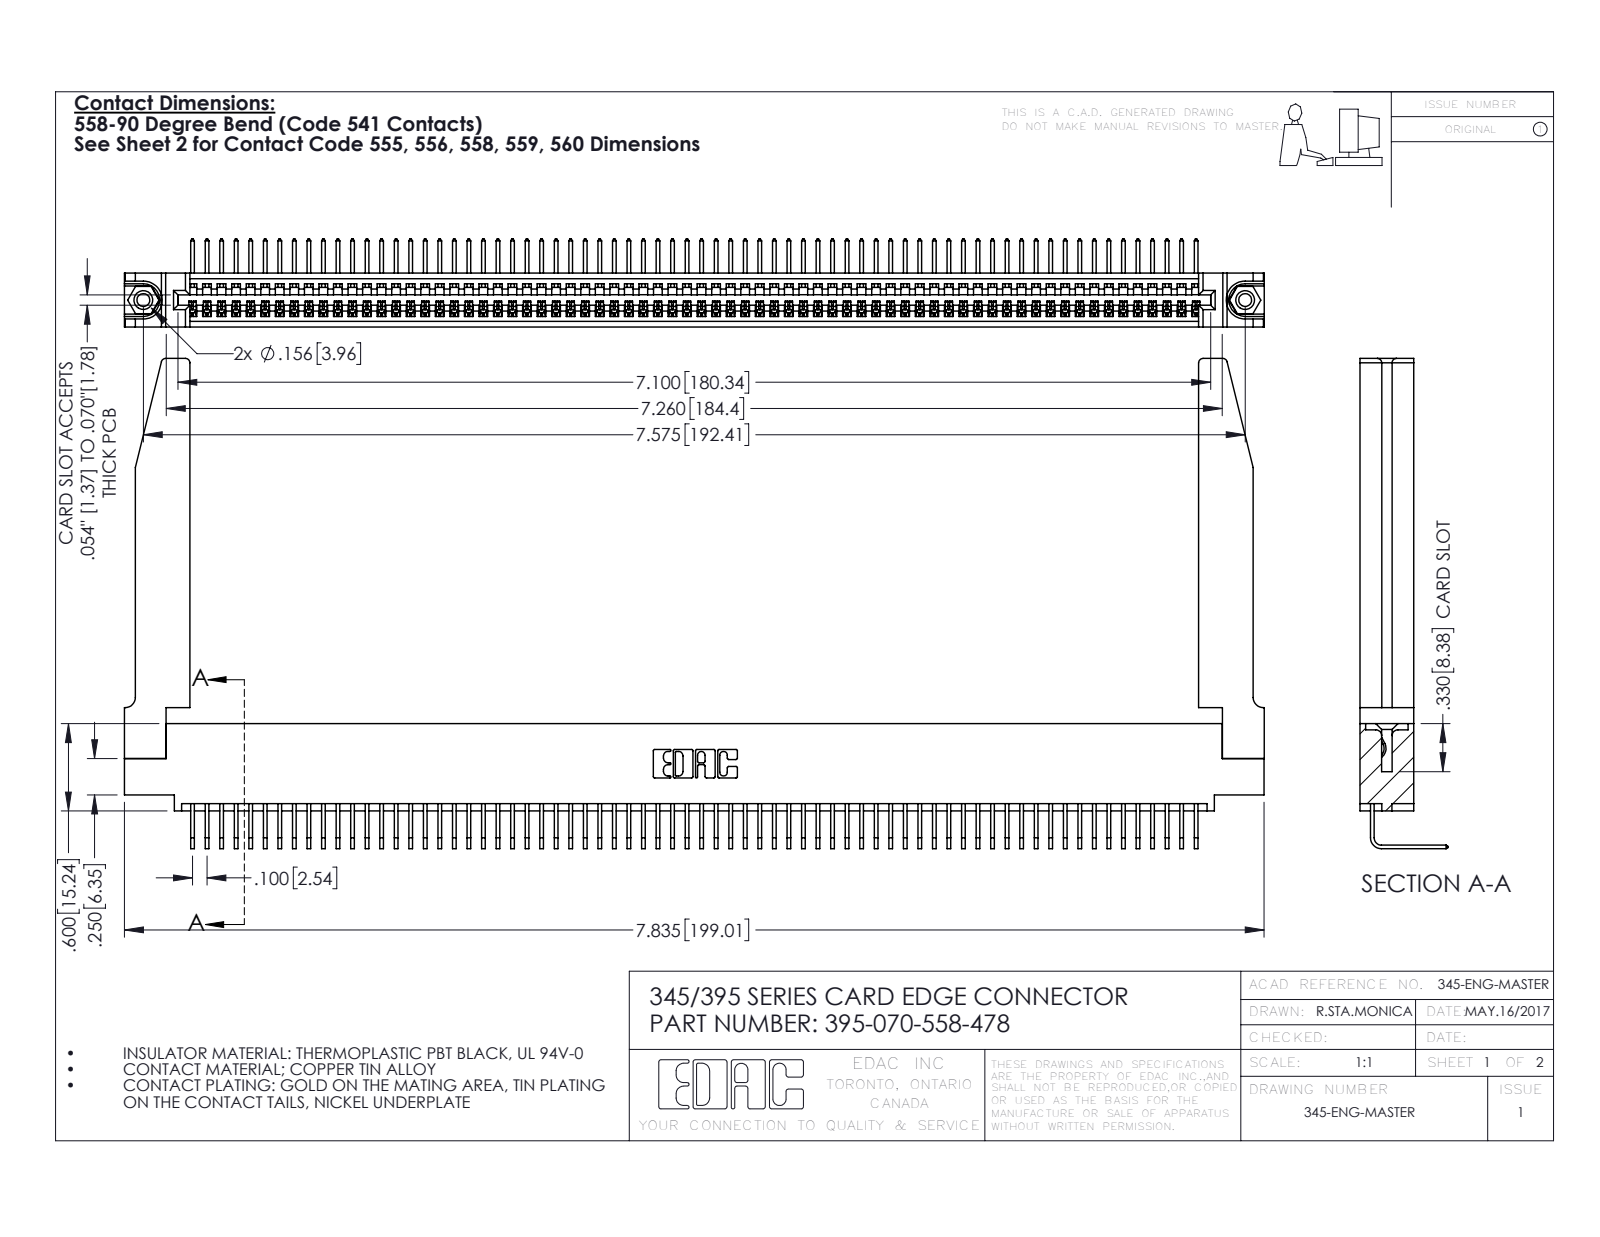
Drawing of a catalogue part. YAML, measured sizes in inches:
part_name: "345-292-001_558 Tail - 2; 345-220-078_345-220-078; 395-070-558-478; 345-250-001_345-250-001-102 (+1 more)"
step_written_by: "SolidWorks 2016 (CONFIG_CONTROL_DESIGN)"
units: inches
bodies: {solids: 75, faces: 4564, planar: 3166, cylindrical: 1346, other: 52}
overall_size: [7.836, 3.369, 0.605]
volume: 1.652
surface_area: 53.19
round_holes:
  - {diameter: 0.089, count: 2}
  - {diameter: 0.125, count: 2}
  - {diameter: 0.156, count: 2}
  - {diameter: 0.064, count: 1}
round_bosses_or_shafts:
  - {diameter: 0.155, count: 2}
partial_cylinders:
  - {radius: 0.006, count: 140}
  - {radius: 0.01, count: 22}
  - {radius: 0.03, count: 8}
  - {radius: 0.007, count: 6}
  - {radius: 0.031, count: 6}
  - {radius: 0.026, count: 3}
  - {radius: 0.031, count: 2}
  - {radius: 0.04, count: 2}
face_to_face_distances: [0.072, 0.37, 0.298, 0.2, 0.098, 0.272, 0.025, 0.225, 0.149, 0.148]
hole_center_spacings: [0.27, 7.339, 7.575]
